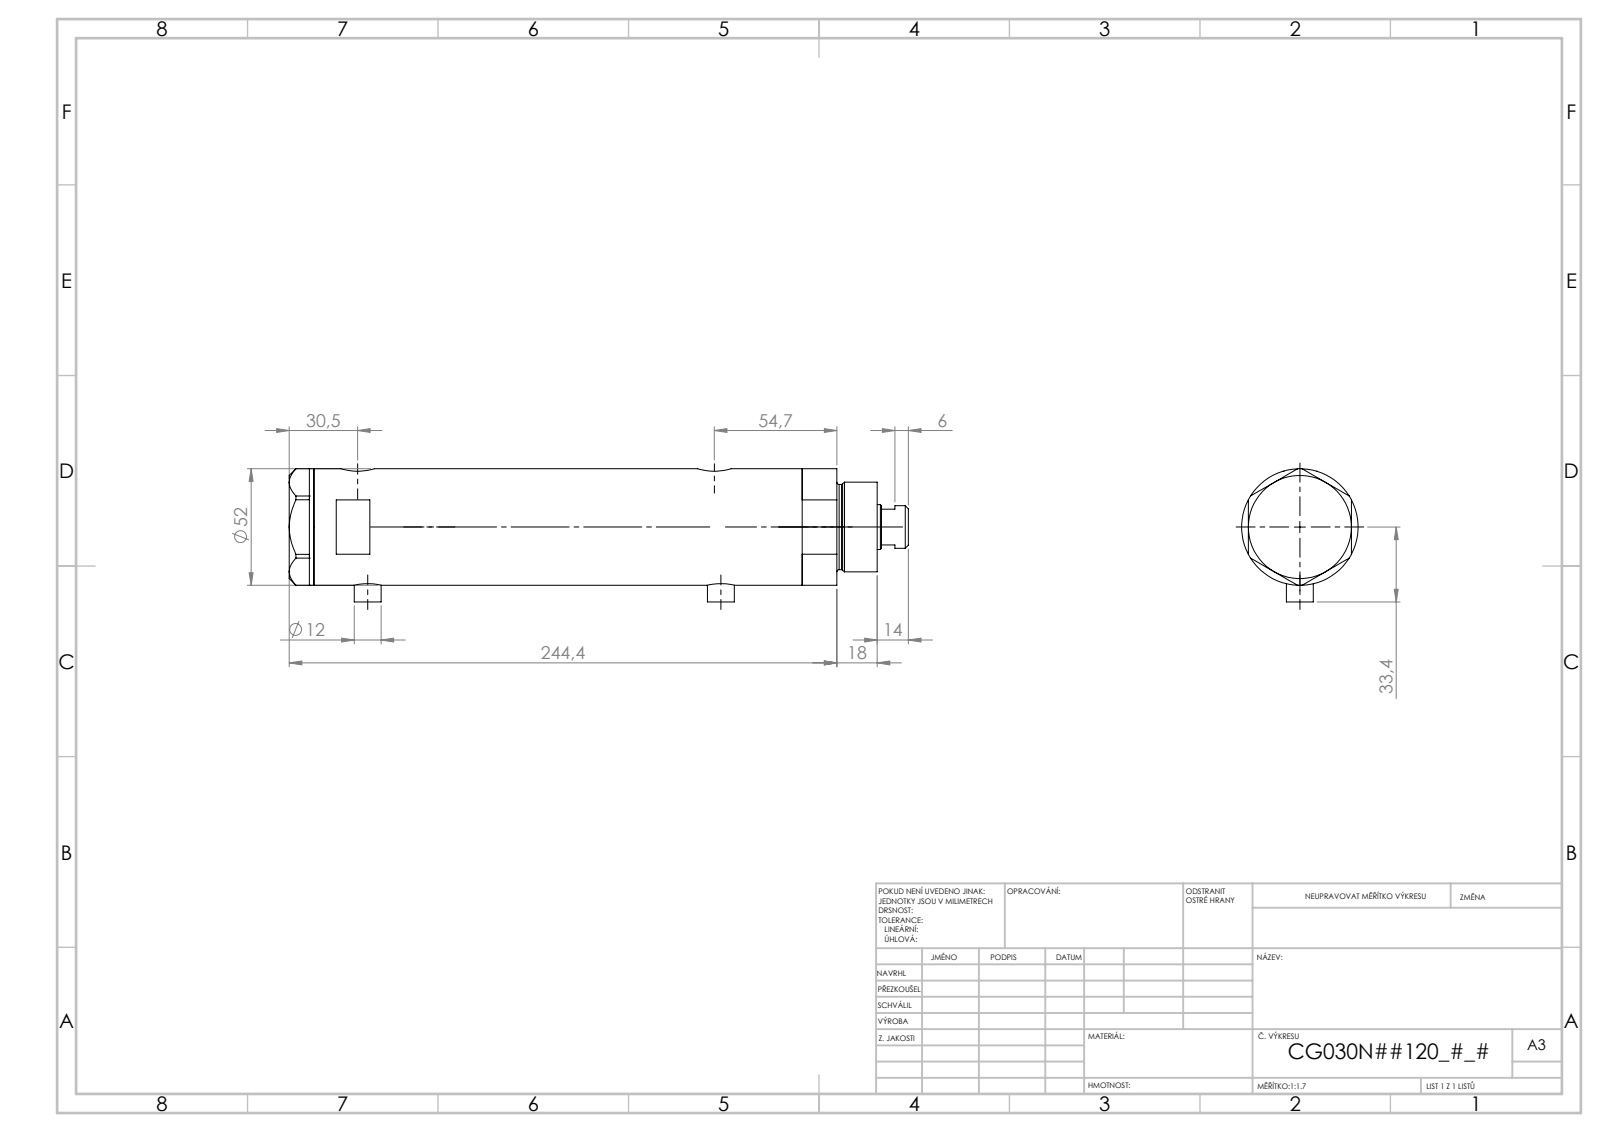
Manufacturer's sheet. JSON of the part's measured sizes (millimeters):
{"part_name": "V270CG_BACK; V270CG_FRONT; V270CG_VC; V270CG_MIDDLE", "step_written_by": "SolidWorks 2019 (CONFIG_CONTROL_DESIGN)", "units": "millimeters", "bodies": {"solids": 4, "faces": 140, "planar": 67, "cylindrical": 53, "other": 20}, "overall_size": [269.02, 53.1, 52], "volume_mm3": 475241, "surface_area_mm2": 103542, "round_holes": [[5, 2], [9.73, 2], [12.5, 2], [15, 2], [6.5, 1], [20, 1], [21.5, 1], [30, 1], [33, 1], [44, 1]], "round_bosses_or_shafts": [[12, 2], [52, 1], [40, 1], [38, 1], [19, 1]], "face_to_face_distances": [23.8, 11, 34.8, 46, 184.54, 173.54, 149.74, 220.94, 209.94, 186.14], "hole_center_spacings": [2.9, 4.5, 146.75, 149.65, 151.25, 154.15, 2.89, 2.91]}
